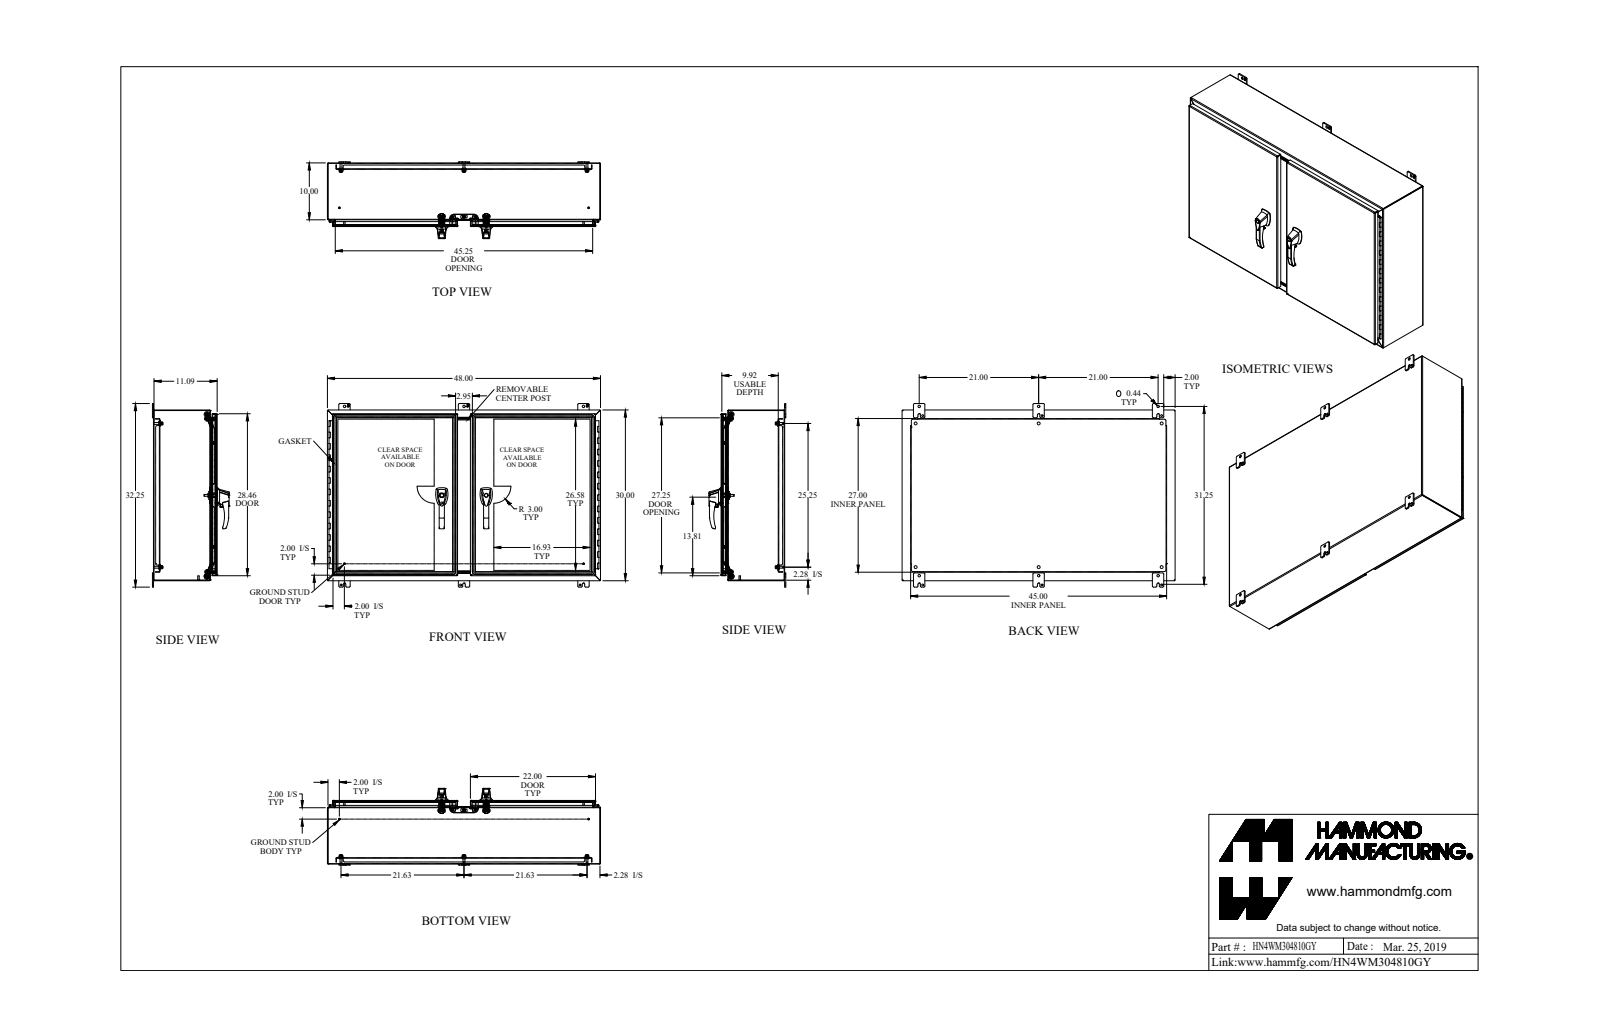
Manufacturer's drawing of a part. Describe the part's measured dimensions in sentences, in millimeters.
The part is named "HN4WM304810GY". Its 3-D file was written by "SolidWorks 2018 (AUTOMOTIVE_DESIGN)". It is 102 solids with 2784 faces: 1305 planar, 1187 cylindrical and 292 other. Overall it measures 1219.2 by 819.2 by 342.6 millimeters. Its volume is 10 980 000 cubic millimeters and its surface area 8 908 000 square millimeters. Round holes: 10 of diameter 7.7, 9 of diameter 8, 8 of diameter 6.4, 6 of diameter 5.1, 6 of diameter 7.8, 6 of diameter 11.3, 6 of diameter 12.7, 4 of diameter 7.1, 4 of diameter 8, 4 of diameter 9.9, 3 of diameter 11.1, 2 of diameter 2.8. Round bosses or shafts: 8 of diameter 25.4, 8 of diameter 7.1, 6 of diameter 16.5, 6 of diameter 9.5, 6 of diameter 8.4, 6 of diameter 7.4, 4 of diameter 19.1, 4 of diameter 15.9. Partial cylindrical surfaces (rounded edges, fillets, slot ends): 37 of radius 3.2, 34 of radius 6.4, 32 of radius 0.5, 28 of radius 4.8, 22 of radius 1.5, 22 of radius 12.7, 19 of radius 1.2, 19 of radius 3.6. The main face-to-face distances are 2.4, 26.2, 2.4, 281.7, 279.3, 23.8, 284.1, 281.7, 253.1, 28.6. The hole center spacings are 152.4, 549.3, 1181.9, 304.8, 844.4, 1211, 641.4, 844.4.
